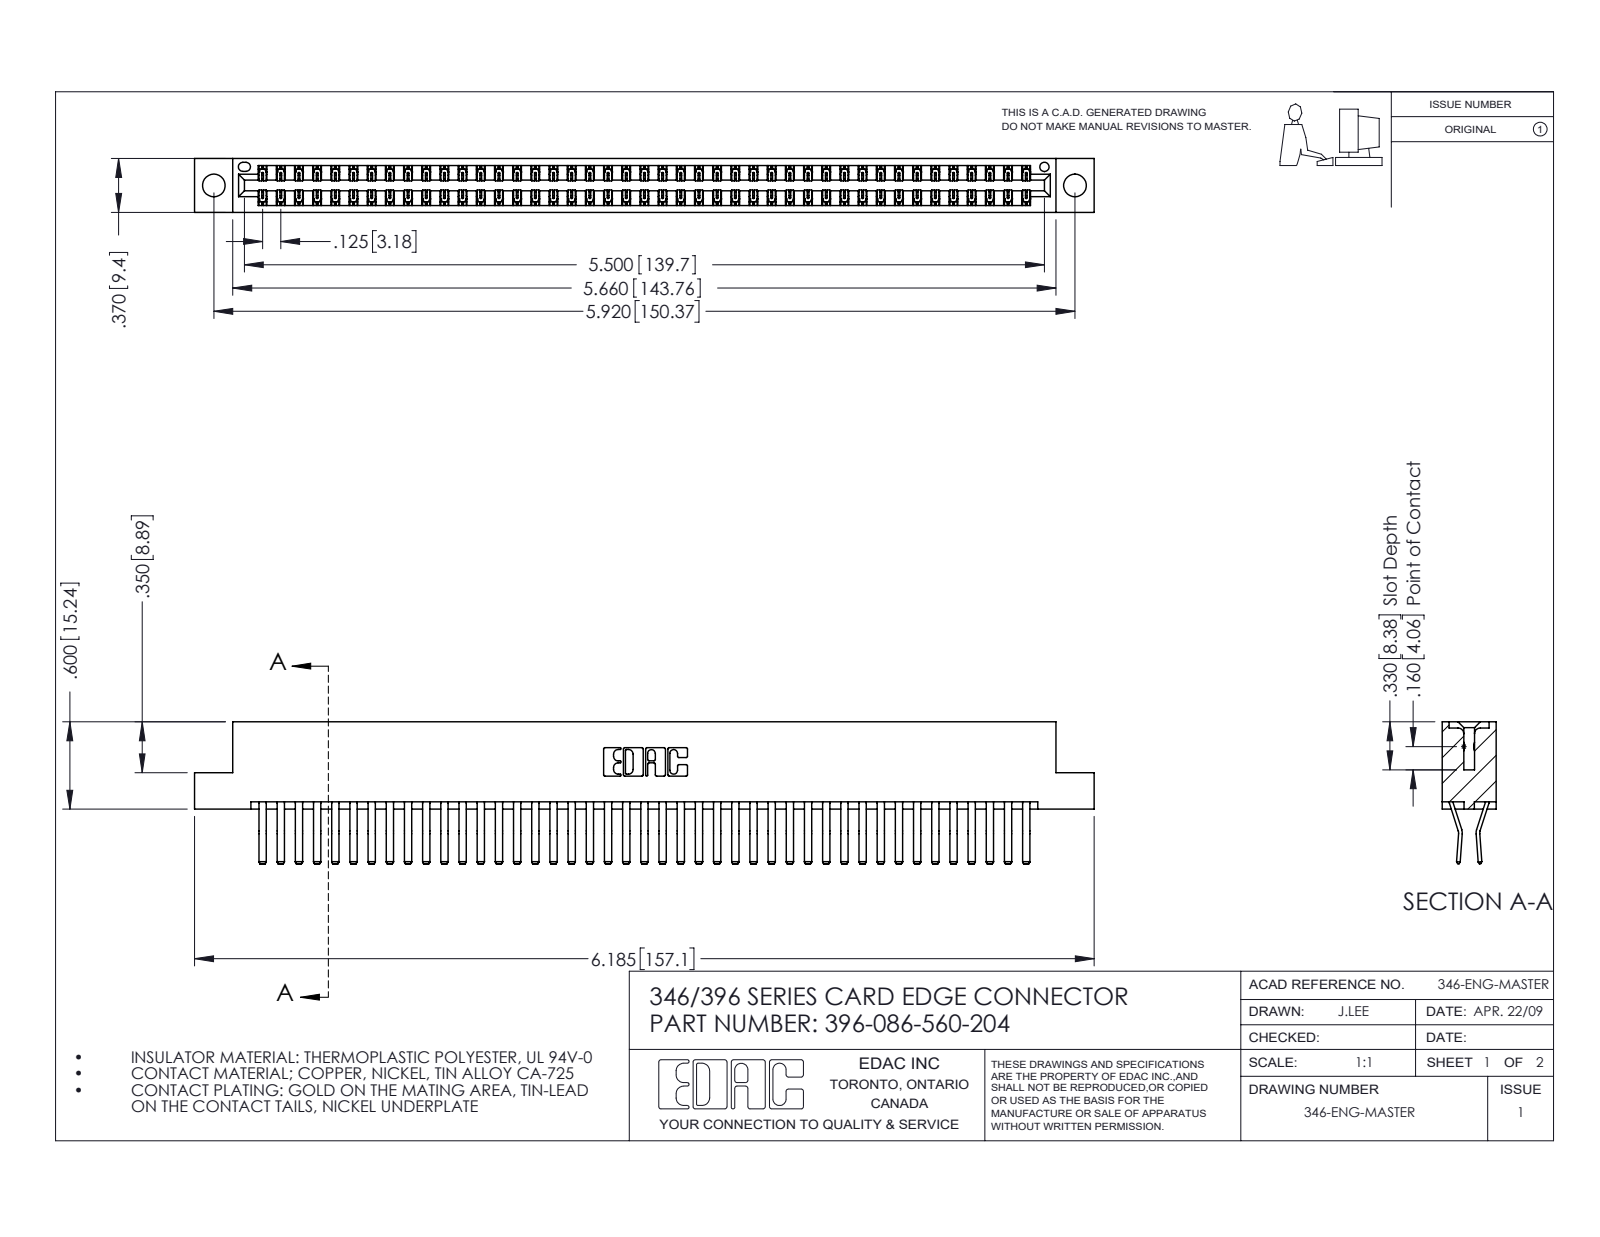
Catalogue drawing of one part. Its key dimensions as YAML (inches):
part_name: "396-086-560-204; 346 Part_Flush Mounting Lugs - 0.156 Dia-TH; 345-292-001_560 Tail"
step_written_by: "SolidWorks 2016 (CONFIG_CONTROL_DESIGN)"
units: inches
bodies: {solids: 87, faces: 4766, planar: 3086, cylindrical: 1680, other: 0}
overall_size: [6.185, 0.975, 0.37]
volume: 0.964
surface_area: 35.74
round_holes:
  - {diameter: 0.156, count: 2}
  - {diameter: 0.064, count: 1}
partial_cylinders:
  - {radius: 0.006, count: 129}
  - {radius: 0.01, count: 22}
  - {radius: 0.007, count: 6}
  - {radius: 0.031, count: 6}
  - {radius: 0.026, count: 3}
  - {radius: 0.01, count: 2}
  - {radius: 0.014, count: 2}
  - {radius: 0.022, count: 2}
face_to_face_distances: [0.048, 0.322, 0.37, 0.025, 0.25, 0.072, 0.298, 0.275, 0.148, 0.222]
hole_center_spacings: [0.246, 5.711, 5.92]
